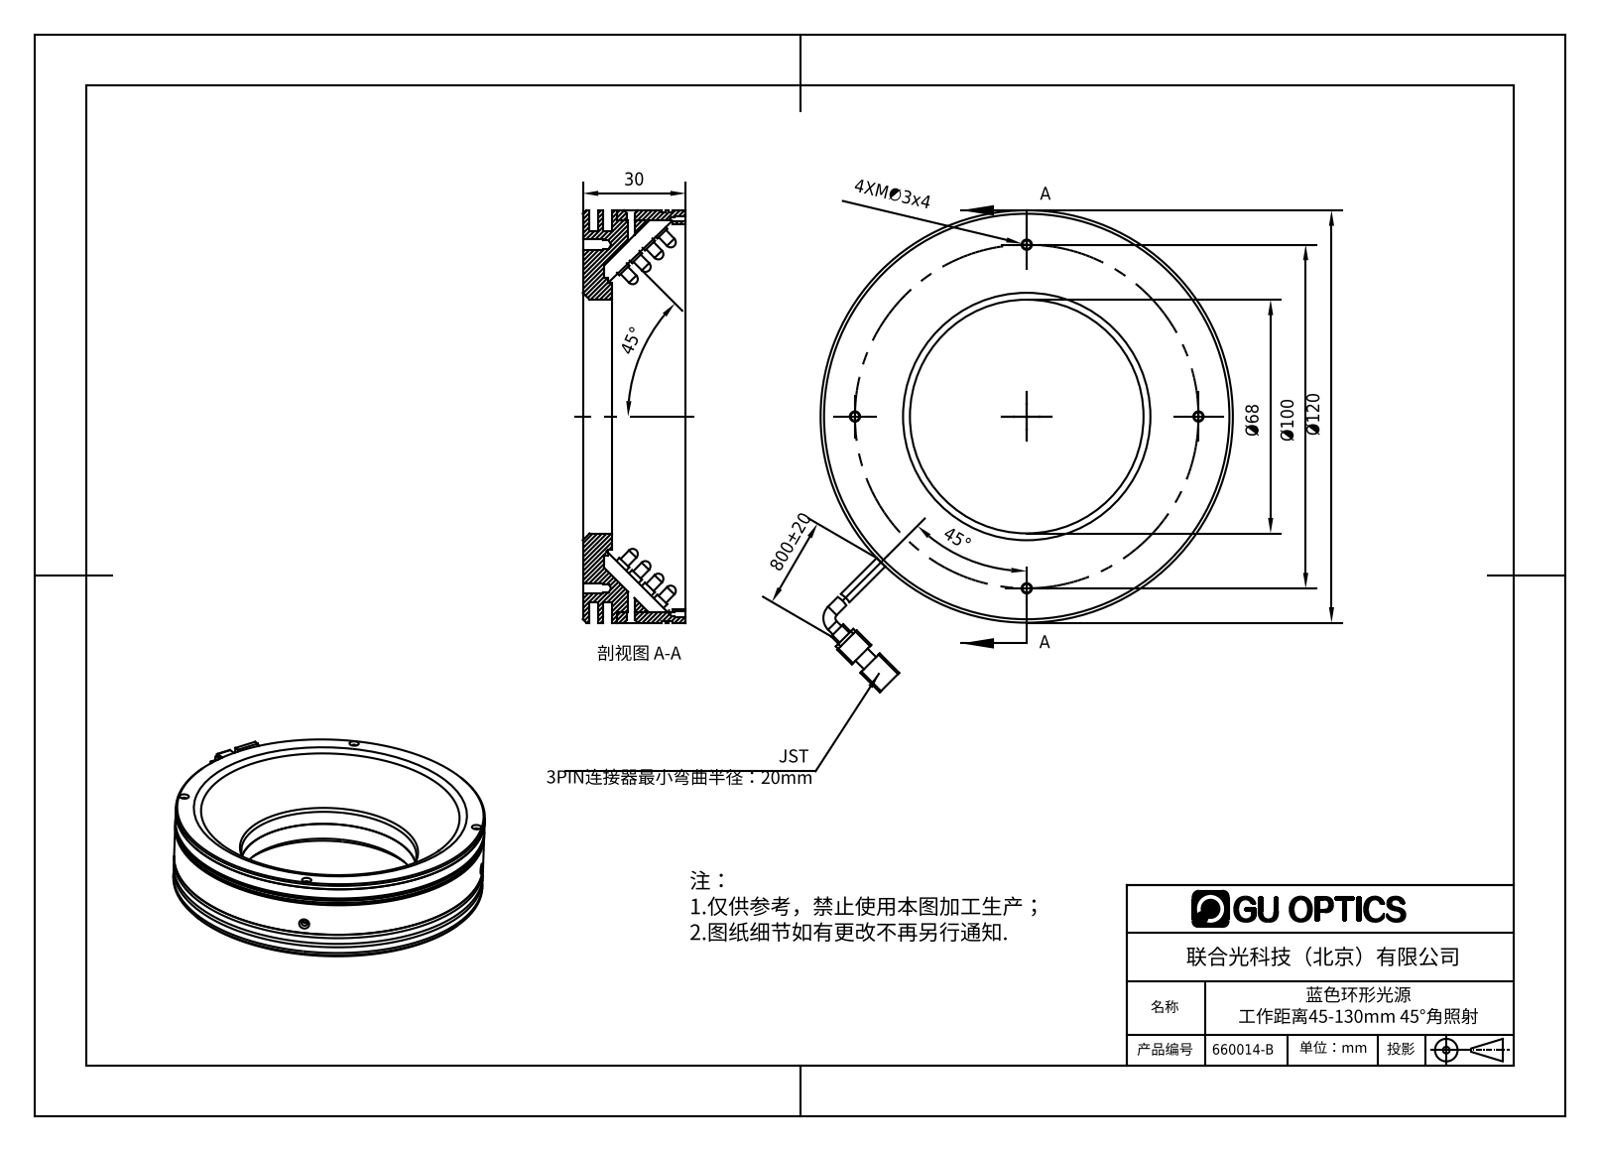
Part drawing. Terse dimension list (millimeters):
name: 660014-B
written by: SolidWorks 2016 (AUTOMOTIVE_DESIGN)
unit: mm
bodies: 266 solids, 4721 faces (3214 planar, 1182 cylindrical, 325 other)
size: 140.26 × 120 × 32
volume: 128 993 mm³; area: 114 112 mm²
holes: 4× ⌀1.2, 4× ⌀1.6, 4× ⌀1.7, 4× ⌀2.5, 4× ⌀3, 4× ⌀3.5, 2× ⌀2, 2× ⌀2.4, 1× ⌀68, 1× ⌀112
bosses: 260× ⌀3.8, 260× ⌀3, 2× ⌀3.5, 1× ⌀120, 1× ⌀119, 1× ⌀114, 1× ⌀108, 1× ⌀81
rounds: 8× R0.5, 4× R1, 1× R1.6, 1× R6
face distances: 4, 30, 2, 2.5, 1.5, 21.5, 8.5, 6, 24, 20
hole spacings: 76.2, 7.5, 50, 57.5, 70.71, 81.32, 107.5, 100
